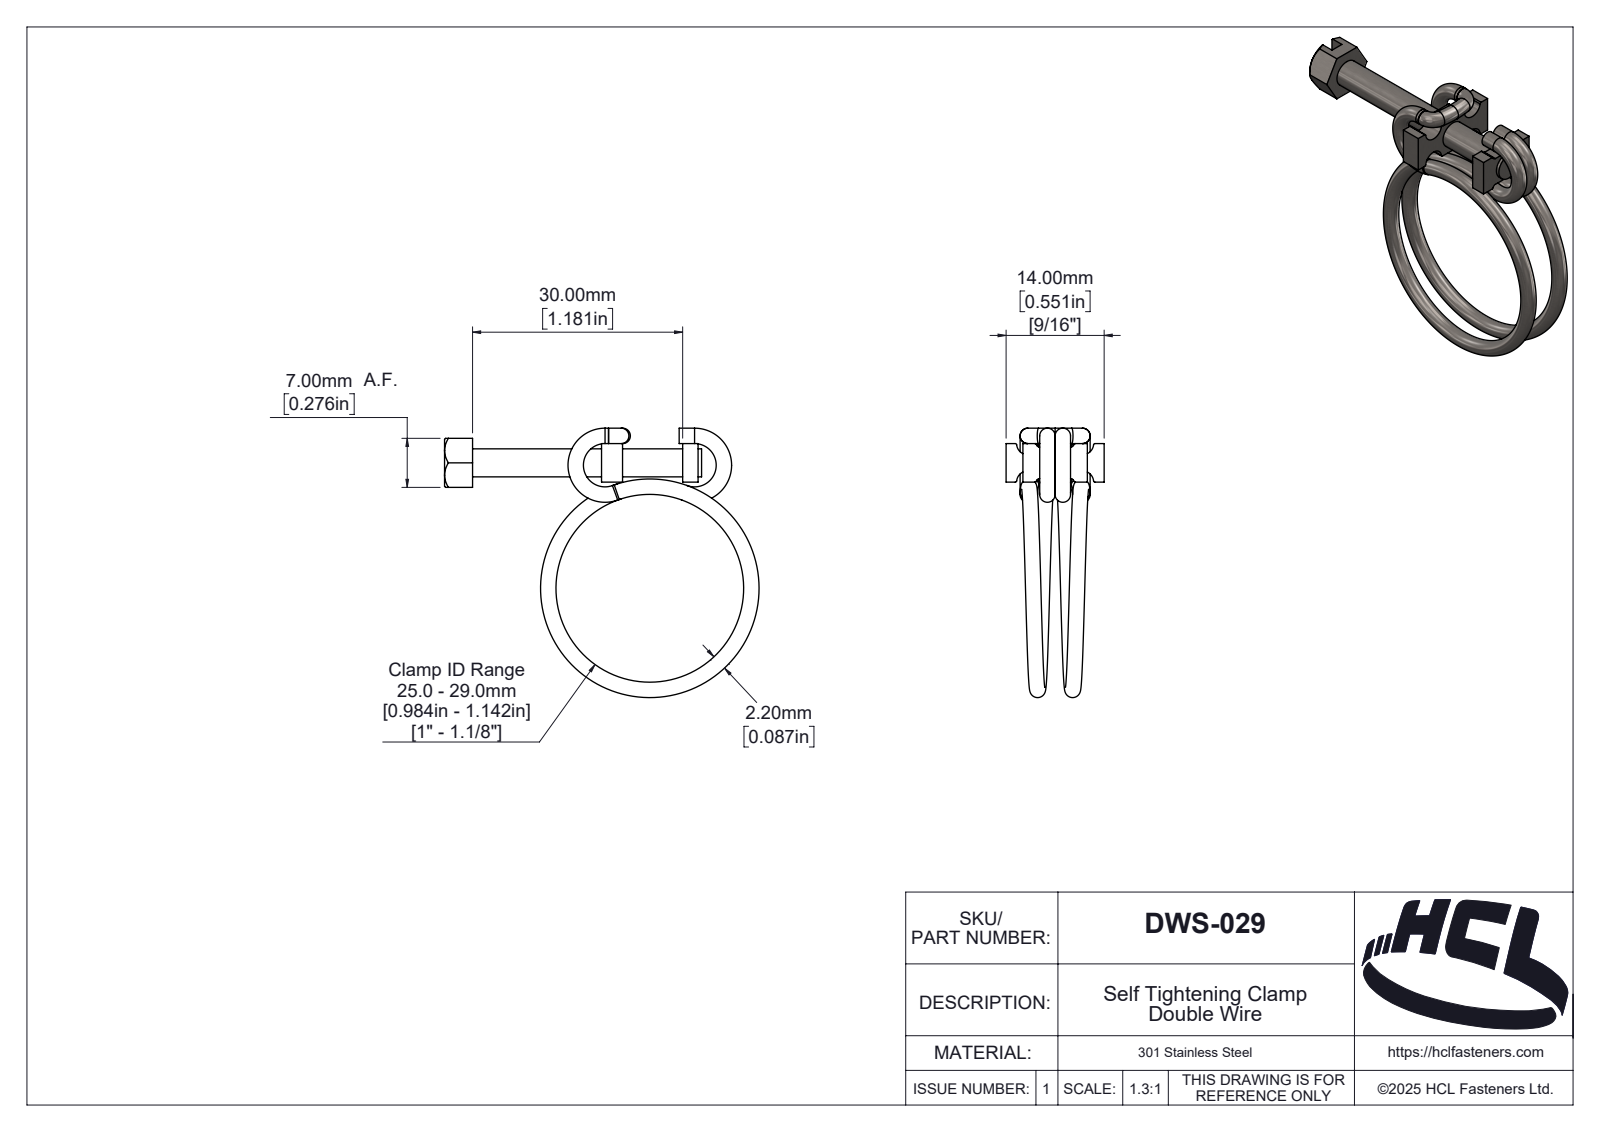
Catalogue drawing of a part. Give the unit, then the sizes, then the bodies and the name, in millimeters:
Units: millimetres
Overall size (bounding box): 44.91 × 38.45 × 14
Round holes (diameter × count): ⌀4 ×1
Round bosses / shafts (diameter × count): ⌀2.2 ×4
Partial cylindrical surfaces — rounded edges, fillets, slot ends (radius × count): R0.2 ×12, R0.5 ×4, R1.6 ×4, R0.4 ×1, R0.51 ×1, R0.53 ×1, R0.64 ×1, R0.91 ×1
Main face-to-face distances: 2, 3, 21.42, 7, 0.5, 11.58, 8.58, 13.78, 10.78, 2.2
Volume: 1 819 mm³ · Surface area: 2 974 mm²
Bodies: 6 solids, 209 faces (51 planar, 74 cylindrical, 84 other)
Part name (STEP PRODUCT): DWS-029
STEP written by: SolidWorks 2025 (AUTOMOTIVE_DESIGN)
